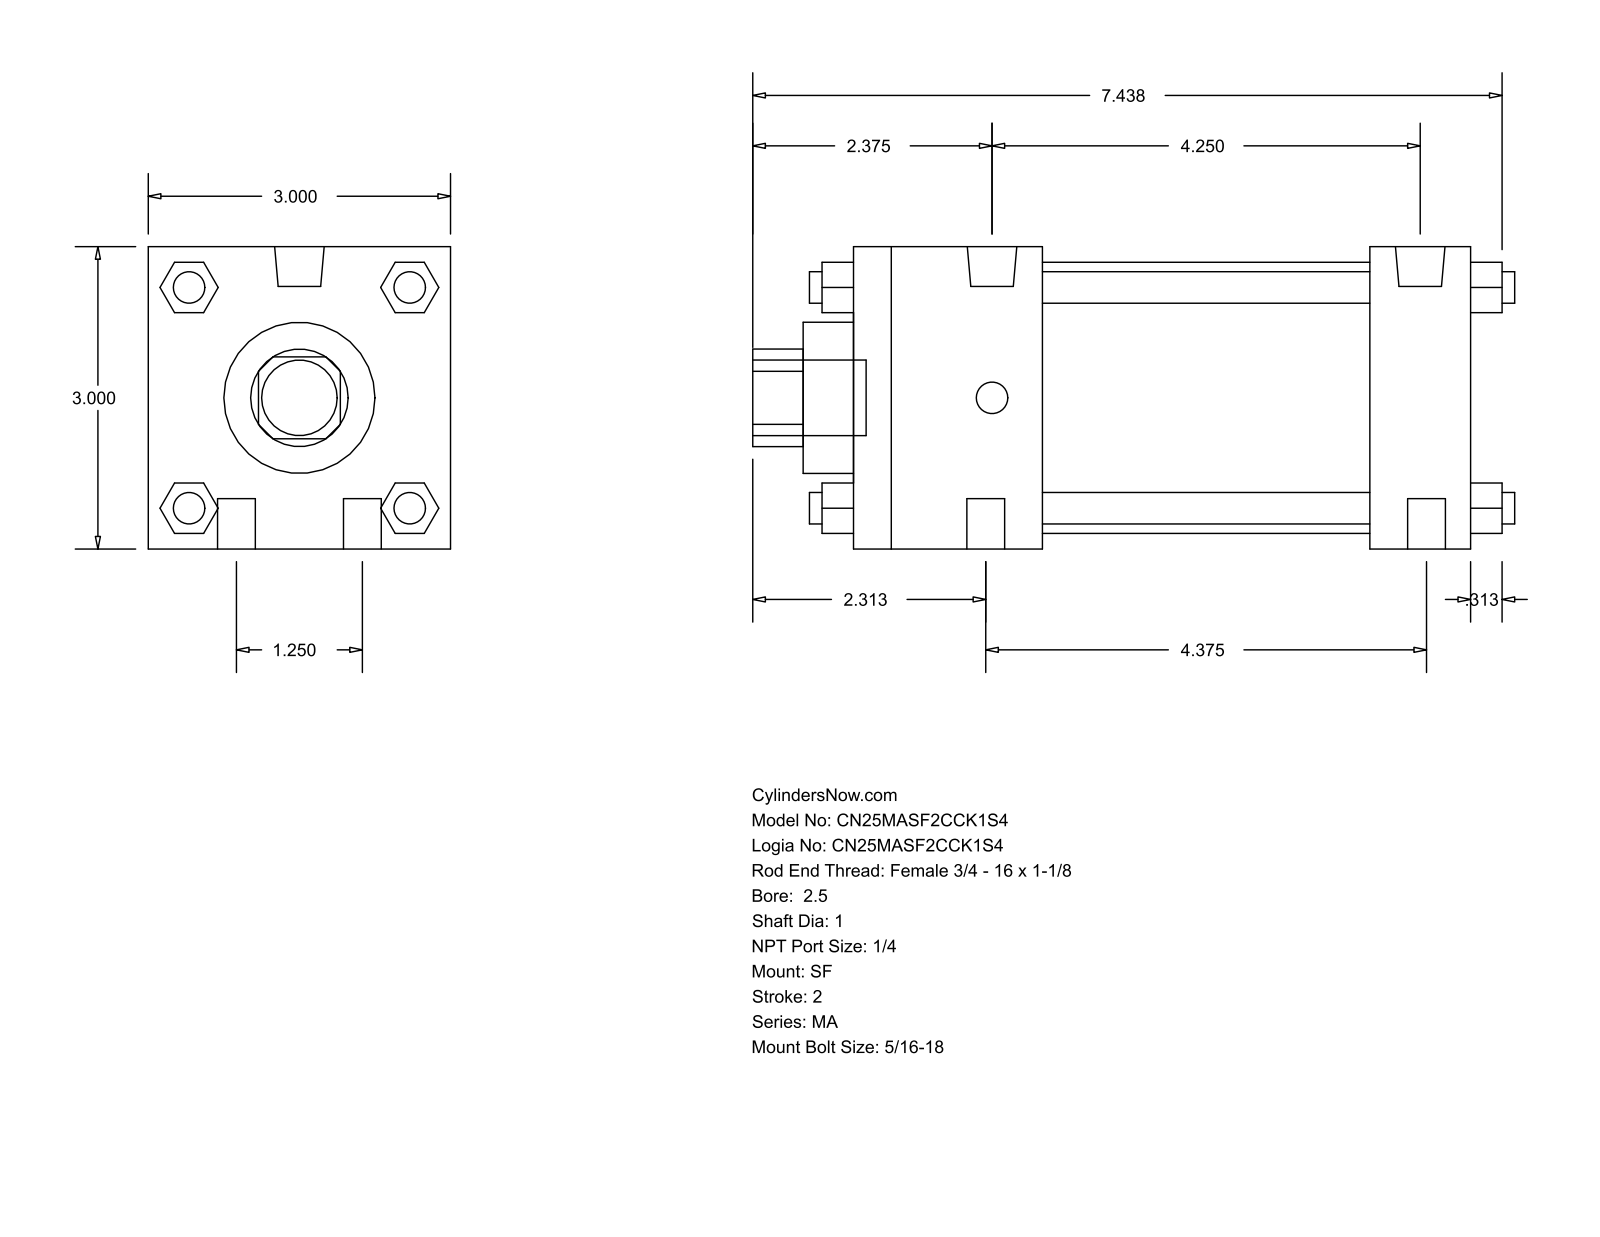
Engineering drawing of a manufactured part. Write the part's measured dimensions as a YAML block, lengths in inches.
part_name: "MA_SF__0250_1"
step_written_by: "GSSL Pune (CONFIG_CONTROL_DESIGN)"
units: inches
bodies: {solids: 0, faces: 124, planar: 94, cylindrical: 30, other: 0}
overall_size: [7.563, 3, 3]
round_holes:
  - {diameter: 1, count: 1}
  - {diameter: 1.5, count: 1}
  - {diameter: 2.69, count: 1}
round_bosses_or_shafts:
  - {diameter: 0.313, count: 6}
  - {diameter: 0.375, count: 4}
  - {diameter: 0.492, count: 2}
  - {diameter: 0.75, count: 1}
partial_cylinders:
  - {radius: 0.484, count: 1}
face_to_face_distances: [3, 6.125, 0.5, 1, 5.125, 1.875, 3.25, 4.25, 1.095, 1.896]
